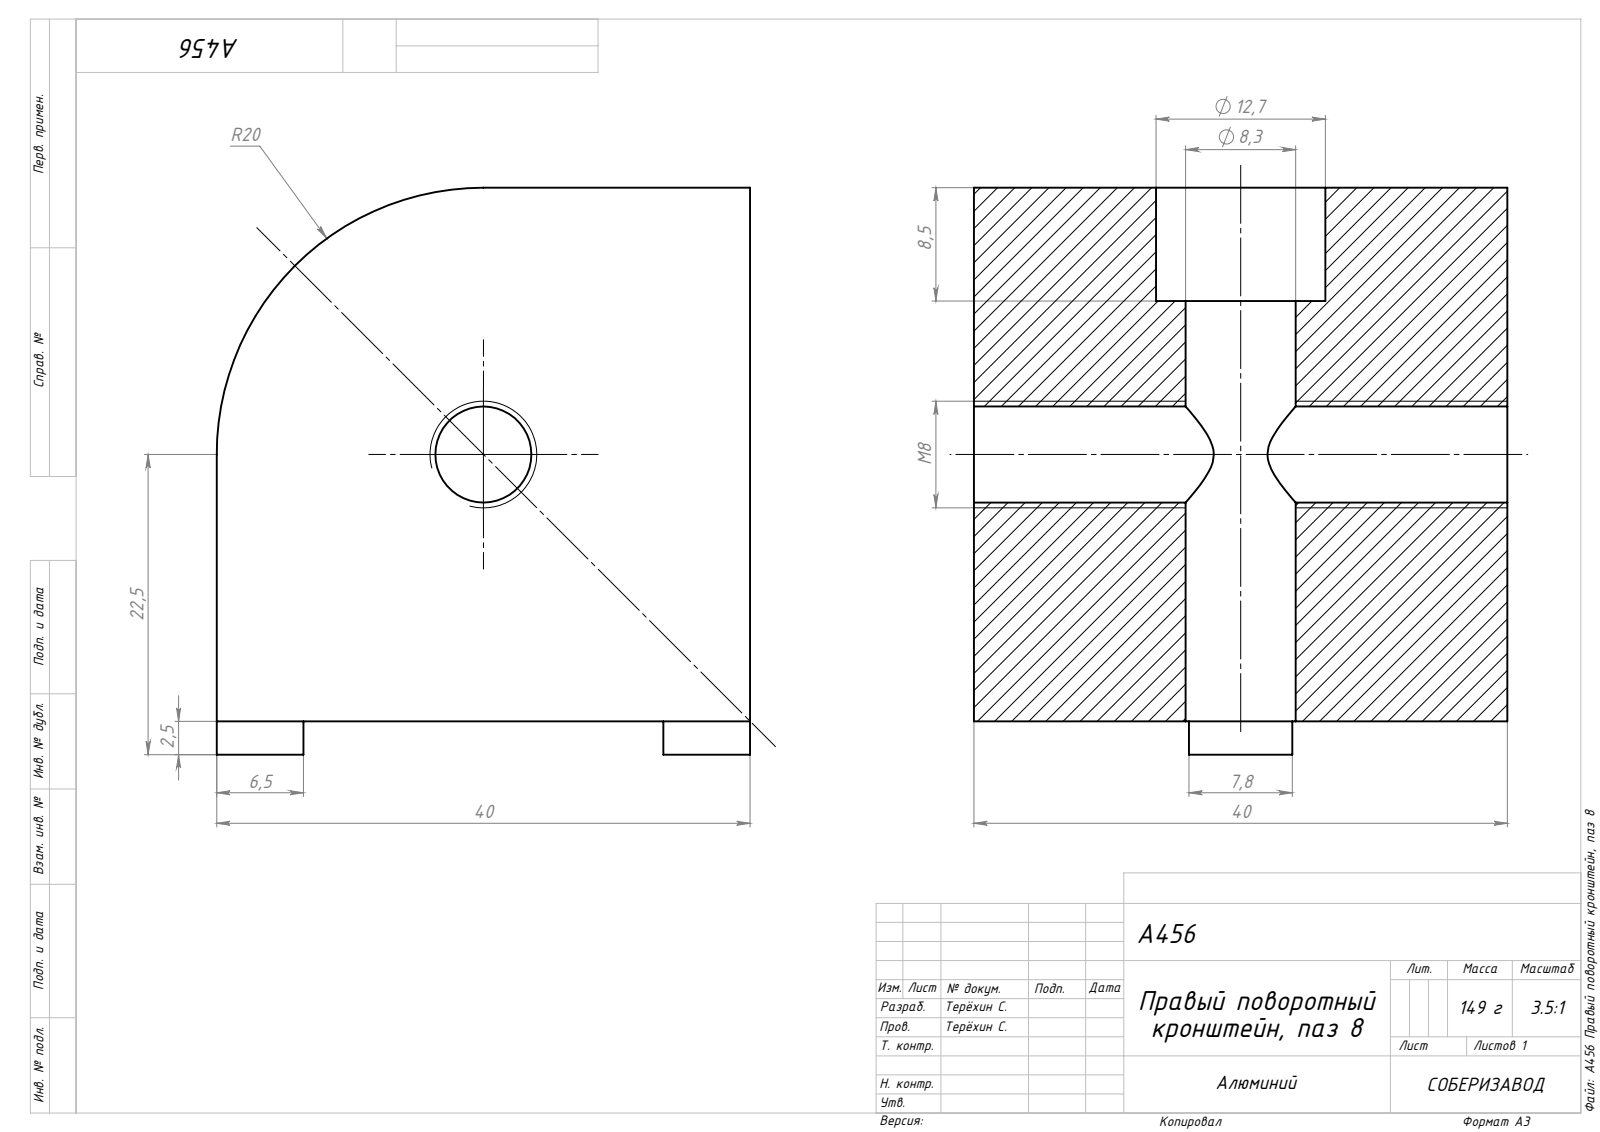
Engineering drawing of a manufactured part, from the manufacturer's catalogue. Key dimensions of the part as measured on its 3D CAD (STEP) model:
Part name (STEP PRODUCT): A456 Правый поворотный кронштейн, паз 8
STEP written by: SolidWorks 2021 (AUTOMOTIVE_DESIGN)
Units: millimetres
Bodies: 1 solid, 24 faces (15 planar, 9 cylindrical, 0 other)
Overall size (bounding box): 42.5 × 40 × 40
Volume: 56 745 mm³ · Surface area: 10 852 mm²
Round holes (diameter × count): ⌀7.2 ×1, ⌀8.25 ×1, ⌀12.7 ×1
Partial cylindrical surfaces — rounded edges, fillets, slot ends (radius × count): R20 ×1
Main face-to-face distances: 40, 2.5, 42.5, 34, 31.5, 8.5, 16.12, 23.88, 6.5, 33.5
